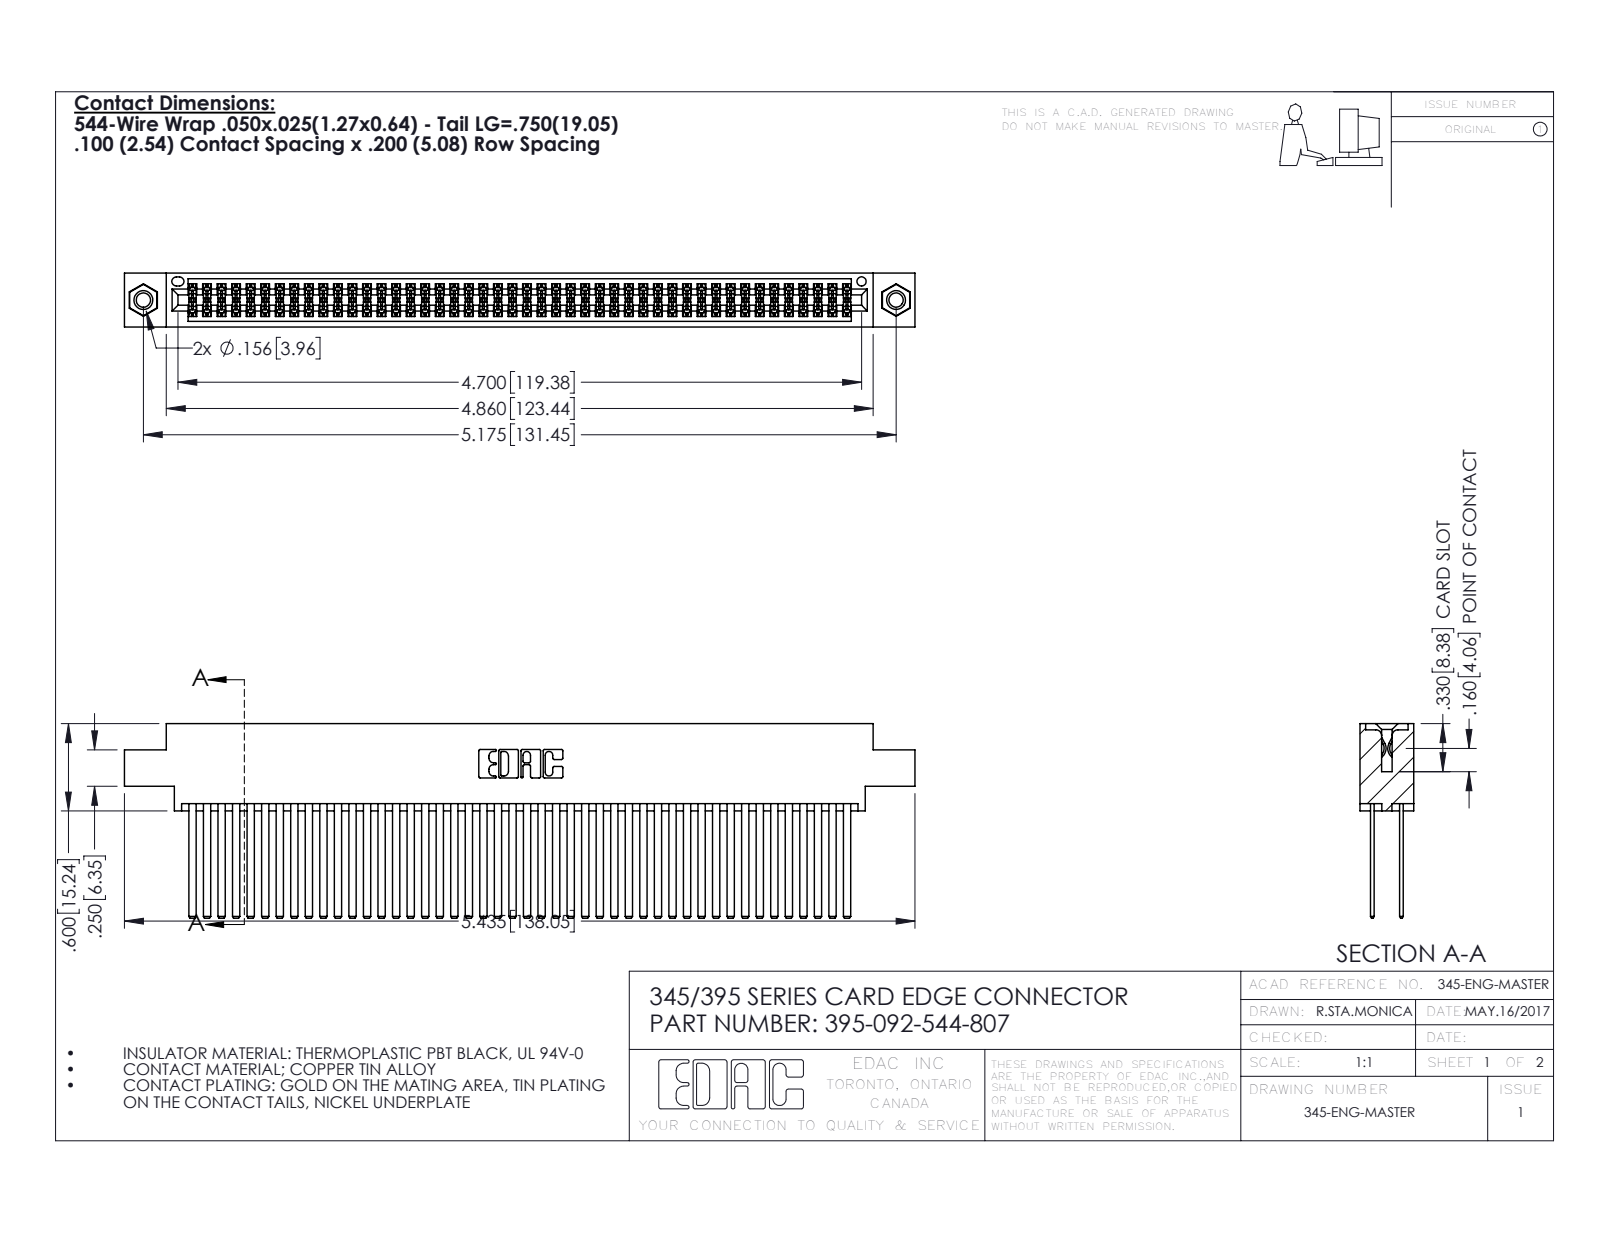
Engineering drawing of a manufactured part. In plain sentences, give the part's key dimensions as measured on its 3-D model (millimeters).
The part is named "395-092-544-807; 345-250-001_345-250-005-103; 345 Part_0.170 Offset - 0.156 Dia-TI; 345-292-001_345-293-144". Its 3-D file was written by "SolidWorks 2016 (CONFIG_CONTROL_DESIGN)". It is 95 solids with 4238 faces: 2784 planar, 1438 cylindrical and 16 other. Overall it measures 138 by 34 by 9.4 millimeters. Its volume is 14 600 cubic millimeters and its surface area 25 630 square millimeters. Round holes: 2 of diameter 2.5, 2 of diameter 3.2, 2 of diameter 4, 1 of diameter 1.6. Round bosses or shafts: 2 of diameter 3.9. Partial cylindrical surfaces (rounded edges, fillets, slot ends): 138 of radius 0.2, 22 of radius 0.3, 6 of radius 0.2, 6 of radius 0.8, 3 of radius 0.7, 2 of radius 0.4, 2 of radius 0.5, 2 of radius 0.6. The main face-to-face distances are 5.1, 0.6, 1.8, 2.5, 6.9, 7.6, 5.7, 4.4, 9.4, 3.8. The hole center spacings are 6.9, 125.5, 131.4.
